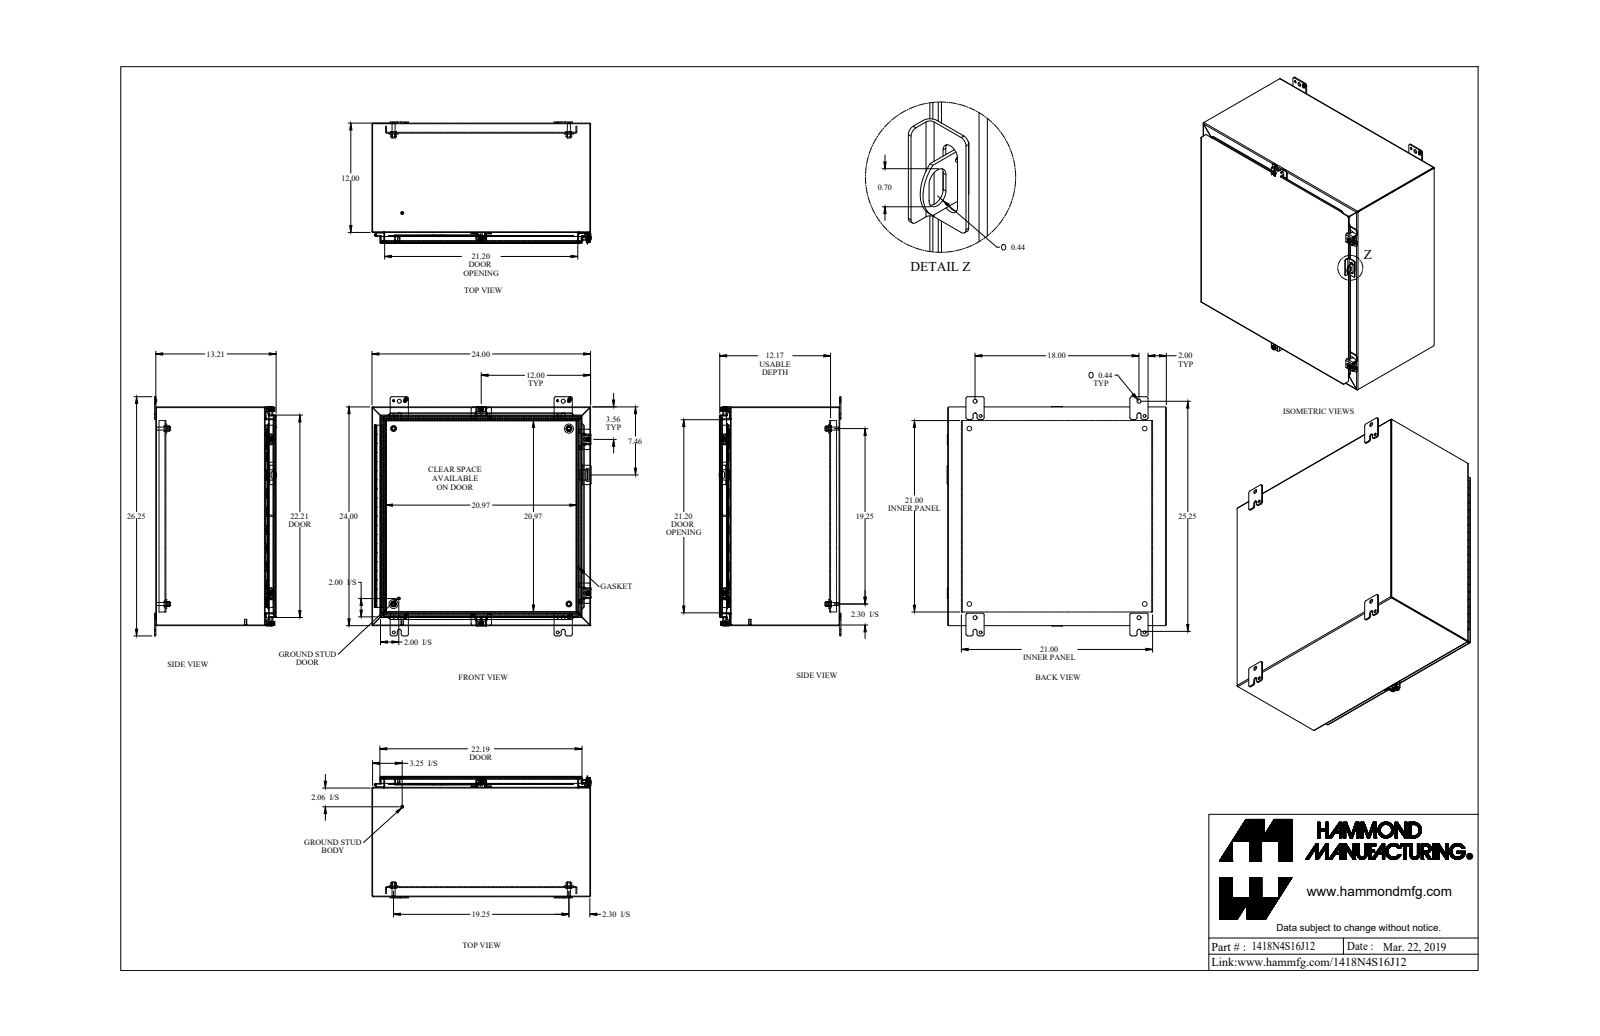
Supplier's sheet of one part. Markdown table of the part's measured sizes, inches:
| quantity | value |
| --- | --- |
| part name | 1418N4S16J12_Default |
| STEP written by | SolidWorks 2019 (CONFIG_CONTROL_DESIGN) |
| units | inches |
| bodies | 41 solids, 1337 faces (730 planar, 481 cylindrical, 126 other) |
| overall size | 26.25 × 24.063 × 13.375 |
| volume | 240.2 in³ |
| surface area | 6 366 in² |
| round holes (diameter × count) | 0.213 × 4, 0.265 × 4, 0.313 × 4, 0.375 × 4, 0.437 × 4, 0.5 × 4, 0.307 × 2, 0.445 × 2, 0.11 × 1, 0.125 × 1 |
| round bosses / shafts (diameter × count) | 0.65 × 4, 0.5 × 4, 0.39 × 4, 0.375 × 4, 0.332 × 4, 0.244 × 4, 1 × 2, 0.313 × 2 |
| partial cylindrical surfaces (radius × count) | 0.188 × 26, 0.036 × 22, 0.108 × 22, 0.048 × 21, 0.143 × 21, 0.25 × 20, 0.125 × 12, 0.045 × 8 |
| main face-to-face distances | 0.072, 23.928, 0.072, 23.856, 24, 13.066, 13.138, 13.138, 13.21, 0.937 |
| hole center spacings | 19.25, 9.857, 18, 1.735, 2.434, 3.065, 20.759, 21.408 |
